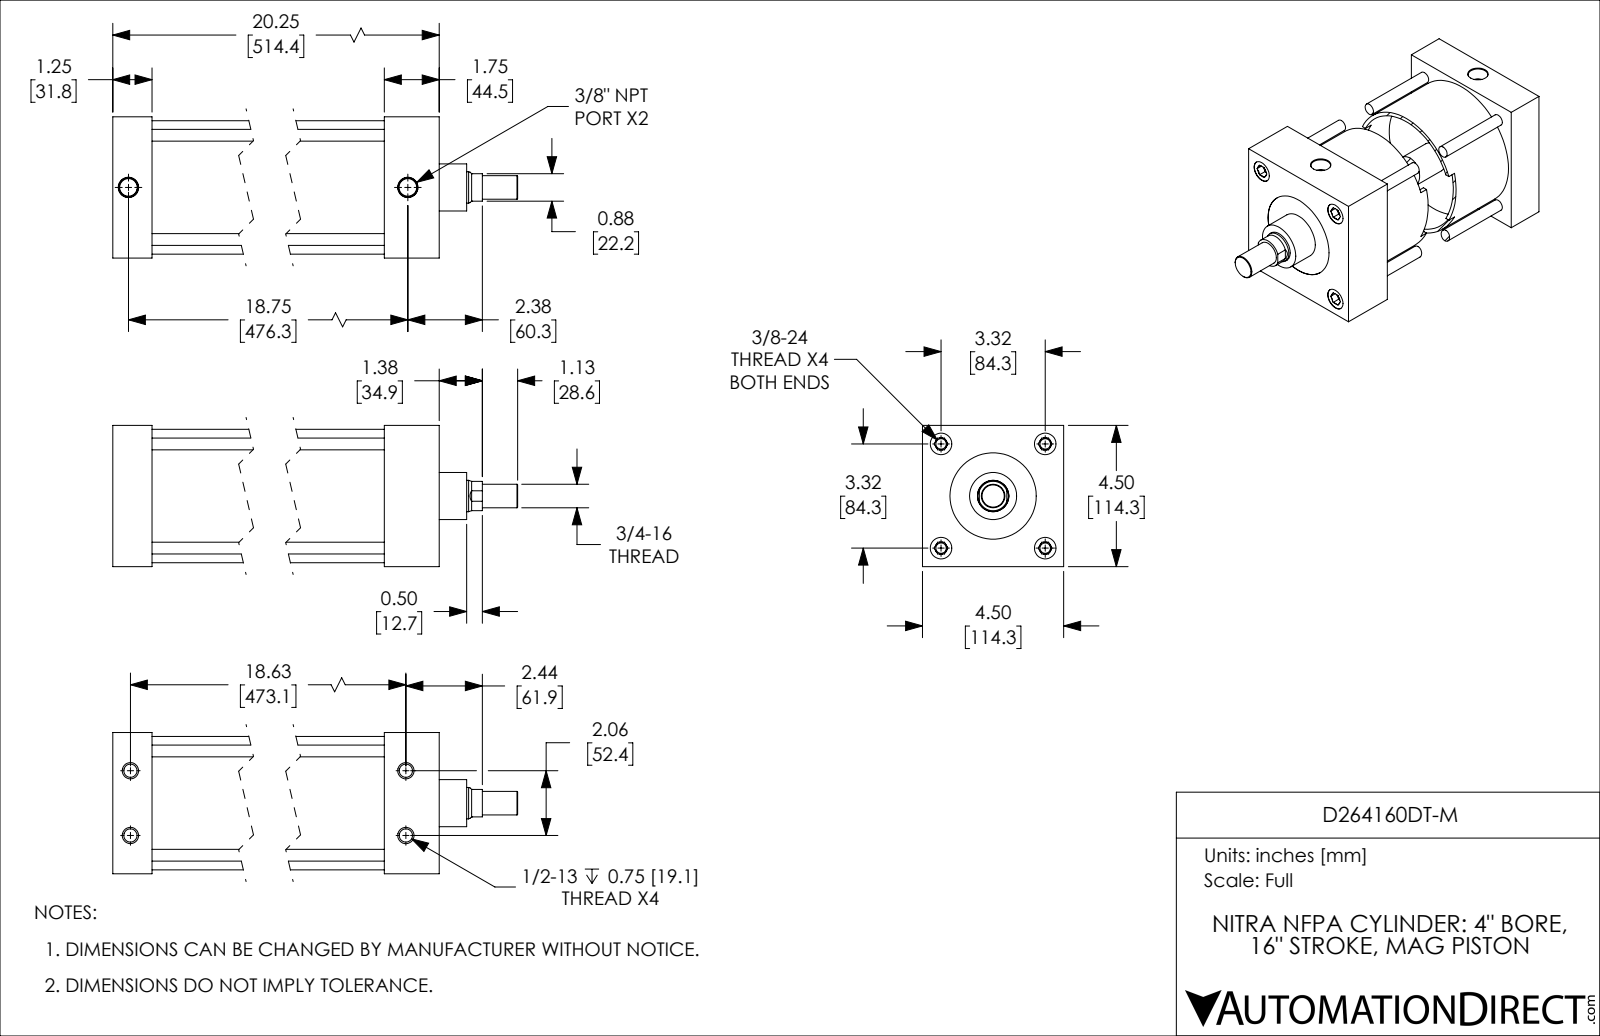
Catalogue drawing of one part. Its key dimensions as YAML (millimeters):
part_name: "D264160DT-M_BODY; D264160DT-M_PISTON_KK1; D264160DT-M"
step_written_by: "SolidWorks 2019 (CONFIG_CONTROL_DESIGN)"
units: millimeters
bodies: {solids: 2, faces: 198, planar: 58, cylindrical: 62, other: 78}
overall_size: [577.9, 114.3, 114.3]
volume: 2042000
surface_area: 511900
round_holes:
  - {diameter: 8.4, count: 4}
  - {diameter: 10.7, count: 4}
  - {diameter: 17.4, count: 4}
  - {diameter: 14.3, count: 2}
  - {diameter: 25.4, count: 1}
  - {diameter: 69.9, count: 1}
  - {diameter: 101.6, count: 1}
round_bosses_or_shafts:
  - {diameter: 9.5, count: 4}
  - {diameter: 108, count: 1}
  - {diameter: 101.6, count: 1}
  - {diameter: 38.1, count: 1}
  - {diameter: 25.4, count: 1}
  - {diameter: 19.1, count: 1}
partial_cylinders:
  - {radius: 11.9, count: 1}
face_to_face_distances: [31.8, 114.3, 469.9, 438.2, 514.4, 482.6, 44.5, 63.5, 406.4, 450.9]
hole_center_spacings: [59.6, 84.3, 475.4, 26.2, 119.3, 473.1, 476, 26.3]
